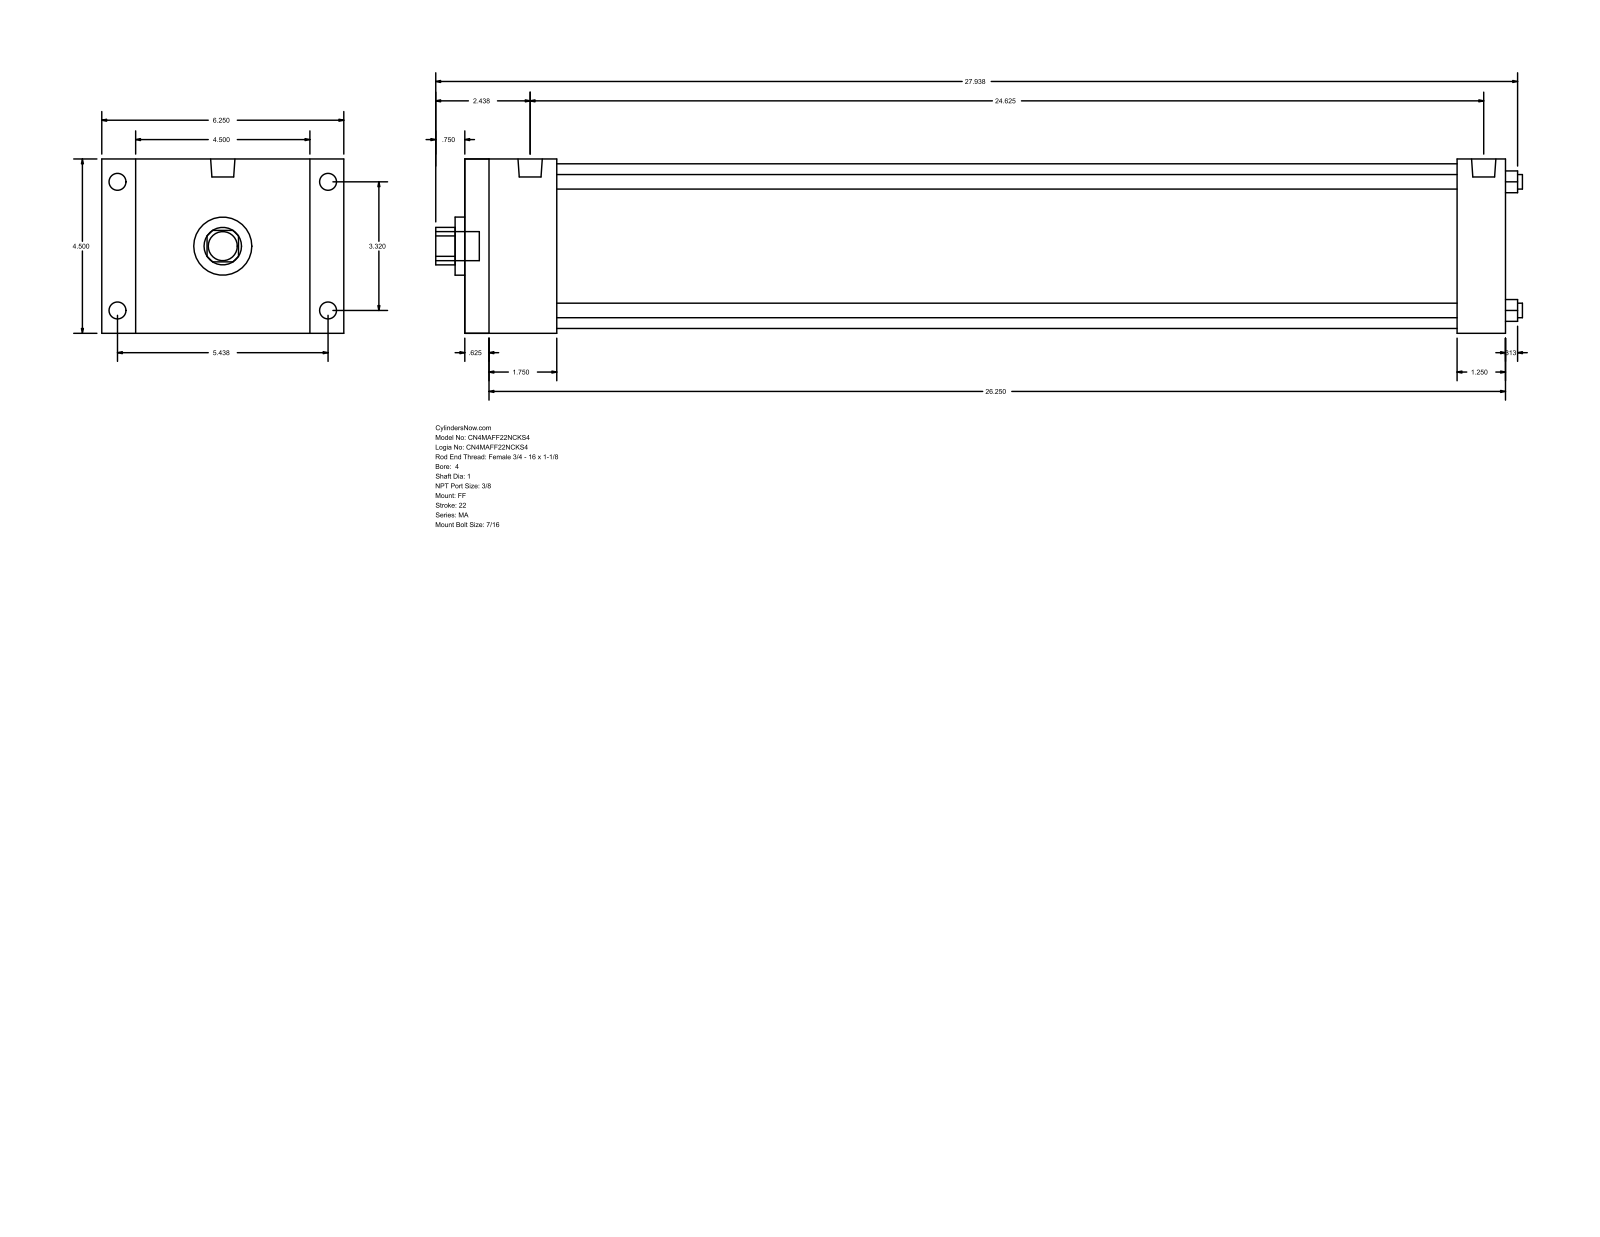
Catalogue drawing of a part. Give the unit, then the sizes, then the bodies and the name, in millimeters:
Units: millimetres
Overall size (bounding box): 712.79 × 158.75 × 114.3
Round holes (diameter × count): ⌀9.53 ×4, ⌀25.4 ×1, ⌀38.1 ×1, ⌀107.95 ×1
Round bosses / shafts (diameter × count): ⌀11.11 ×8, ⌀15.93 ×2, ⌀19.05 ×1
Partial cylindrical surfaces — rounded edges, fillets, slot ends (radius × count): R12.29 ×1
Main face-to-face distances: 114.3, 682.62, 15.87, 666.75, 22.23, 136.53, 650.87, 635, 31.75, 60.33
Hole centre spacings: 59.62, 84.32, 119.25
Bodies: 0 solids, 92 faces (64 planar, 28 cylindrical, 0 other)
Part name (STEP PRODUCT): MA_FF__0400_1
STEP written by: GSSL Pune (CONFIG_CONTROL_DESIGN)
